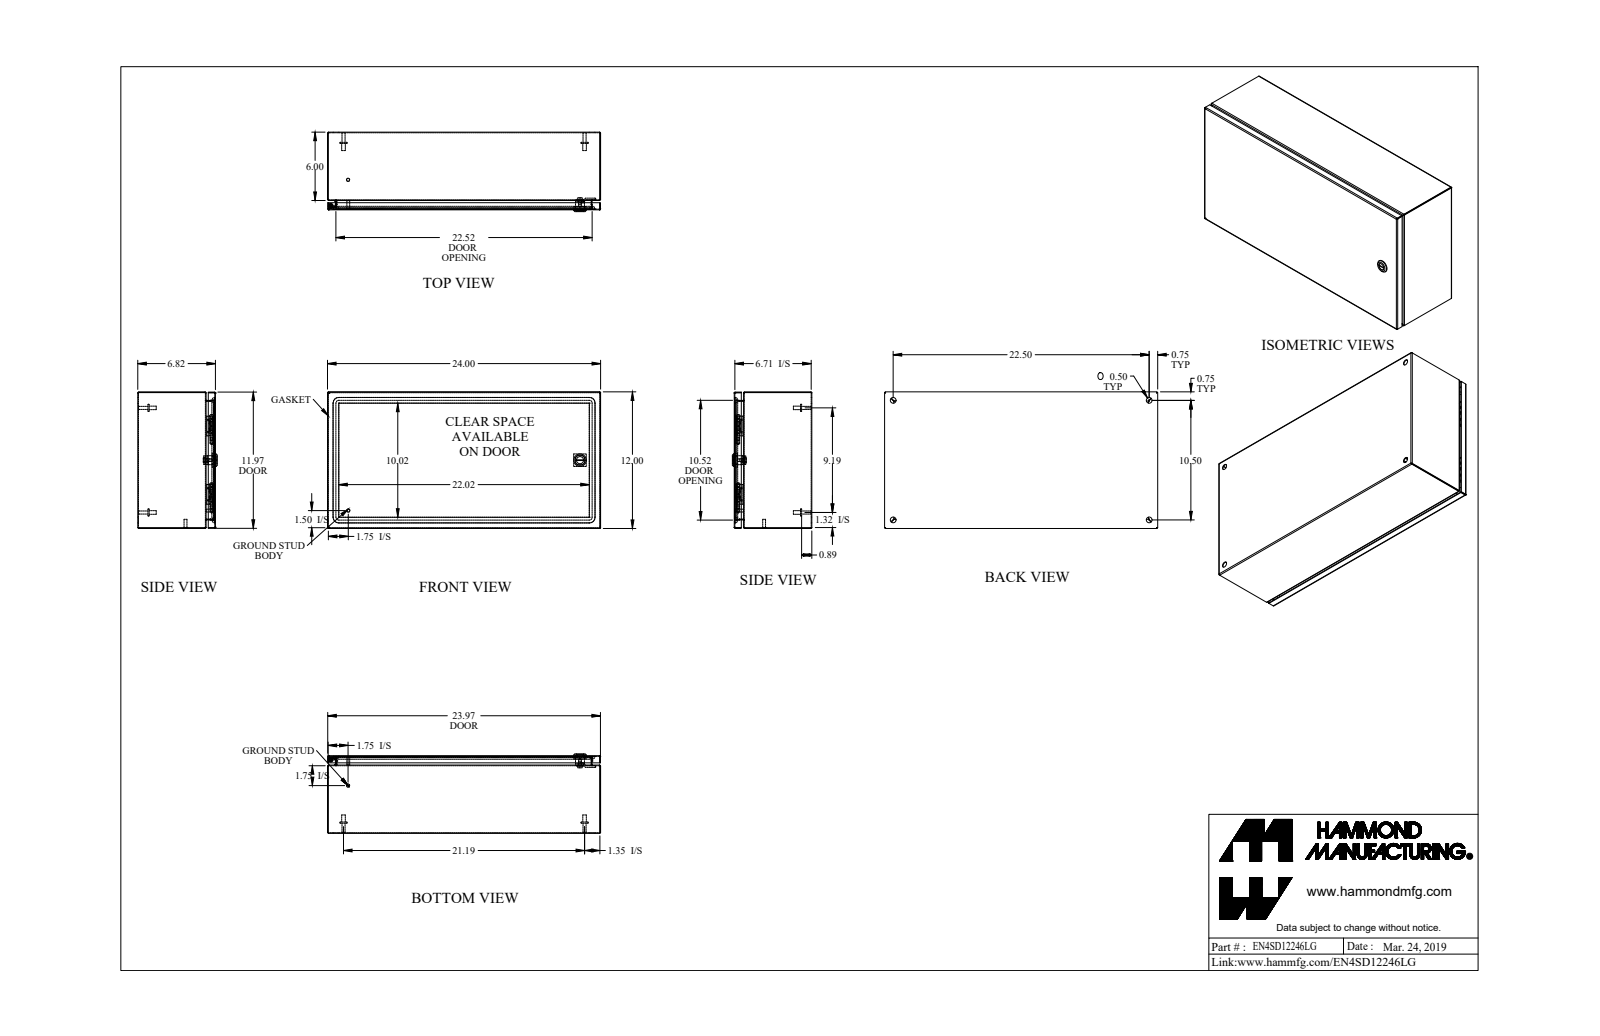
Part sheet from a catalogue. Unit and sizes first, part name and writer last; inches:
Units: inches
Overall size (bounding box): 24 × 12 × 6.982
Round holes (diameter × count): ⌀0.5 ×4, ⌀0.172 ×1, ⌀0.232 ×1, ⌀0.24 ×1, ⌀0.242 ×1, ⌀0.625 ×1, ⌀0.785 ×1
Round bosses / shafts (diameter × count): ⌀0.625 ×4, ⌀0.313 ×4, ⌀0.27 ×4, ⌀0.281 ×2, ⌀0.25 ×2, ⌀1.1 ×1, ⌀0.525 ×1, ⌀0.455 ×1
Partial cylindrical surfaces — rounded edges, fillets, slot ends (radius × count): R0.029 ×21, R0.086 ×21, R0.25 ×16, R19 ×8, R0.006 ×4, R0.062 ×4, R0.499 ×4, R0.125 ×2
Main face-to-face distances: 0.057, 6.765, 6.708, 6.822, 11.943, 11.886, 12, 23.943, 0.822, 5.943
Hole centre spacings: 10.5, 22.074, 22.5, 24.83, 5.356, 5.356
Volume: 72.64 in³ · Surface area: 2 457 in²
Bodies: 21 solids, 634 faces (285 planar, 213 cylindrical, 136 other)
Part name (STEP PRODUCT): EN4SD12246LG_Default
STEP written by: SolidWorks 2019 (CONFIG_CONTROL_DESIGN)
